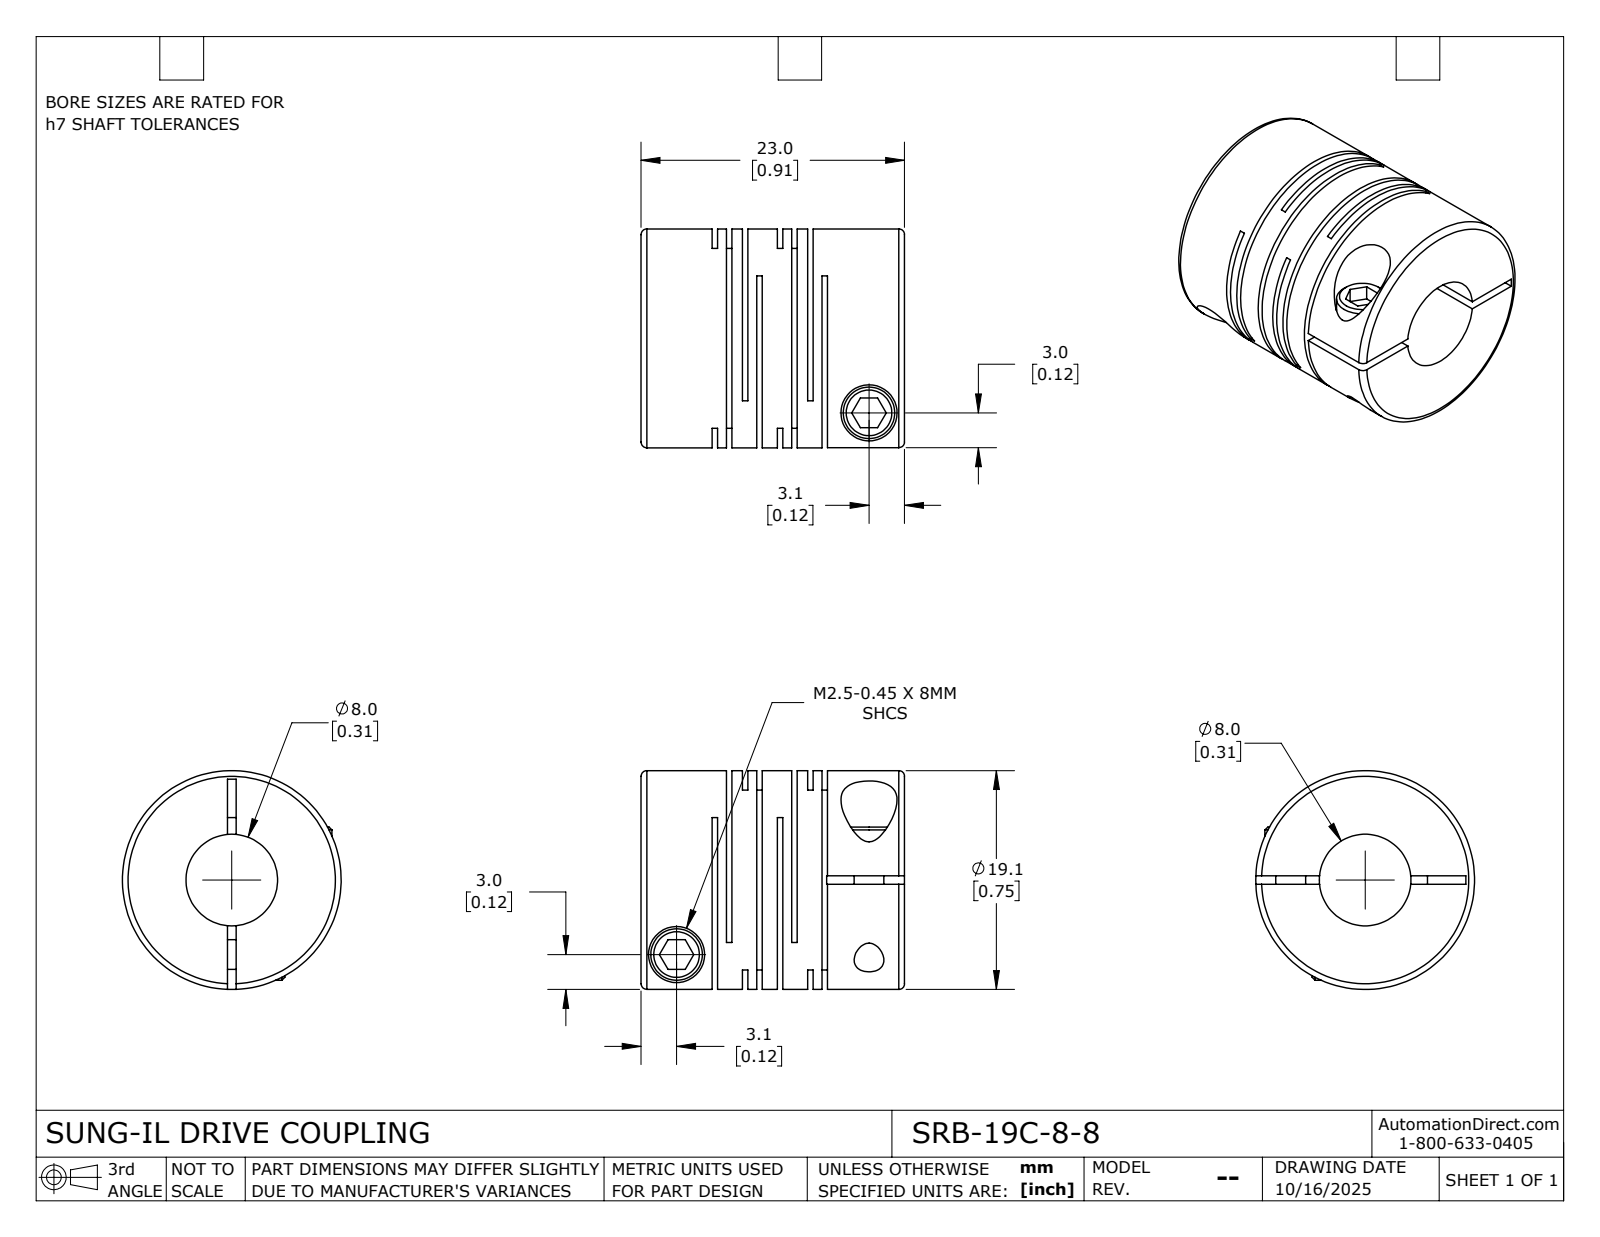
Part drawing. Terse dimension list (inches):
name: SRB-19C-8-8
written by: SolidWorks 2024 (CONFIG_CONTROL_DESIGN)
unit: in
bodies: 1 solid, 115 faces (60 planar, 42 cylindrical, 13 other)
size: 0.906 × 0.752 × 0.752
volume: 0.273 in³; area: 8.824 in²
holes: 2× ⌀0.102, 2× ⌀0.193, 1× ⌀0.315
bosses: 2× ⌀0.177, 1× ⌀0.752
face distances: 0.104, 0.019, 0.049, 0.224, 0.085, 0.12, 0.206, 0.03, 0.175, 0.055
